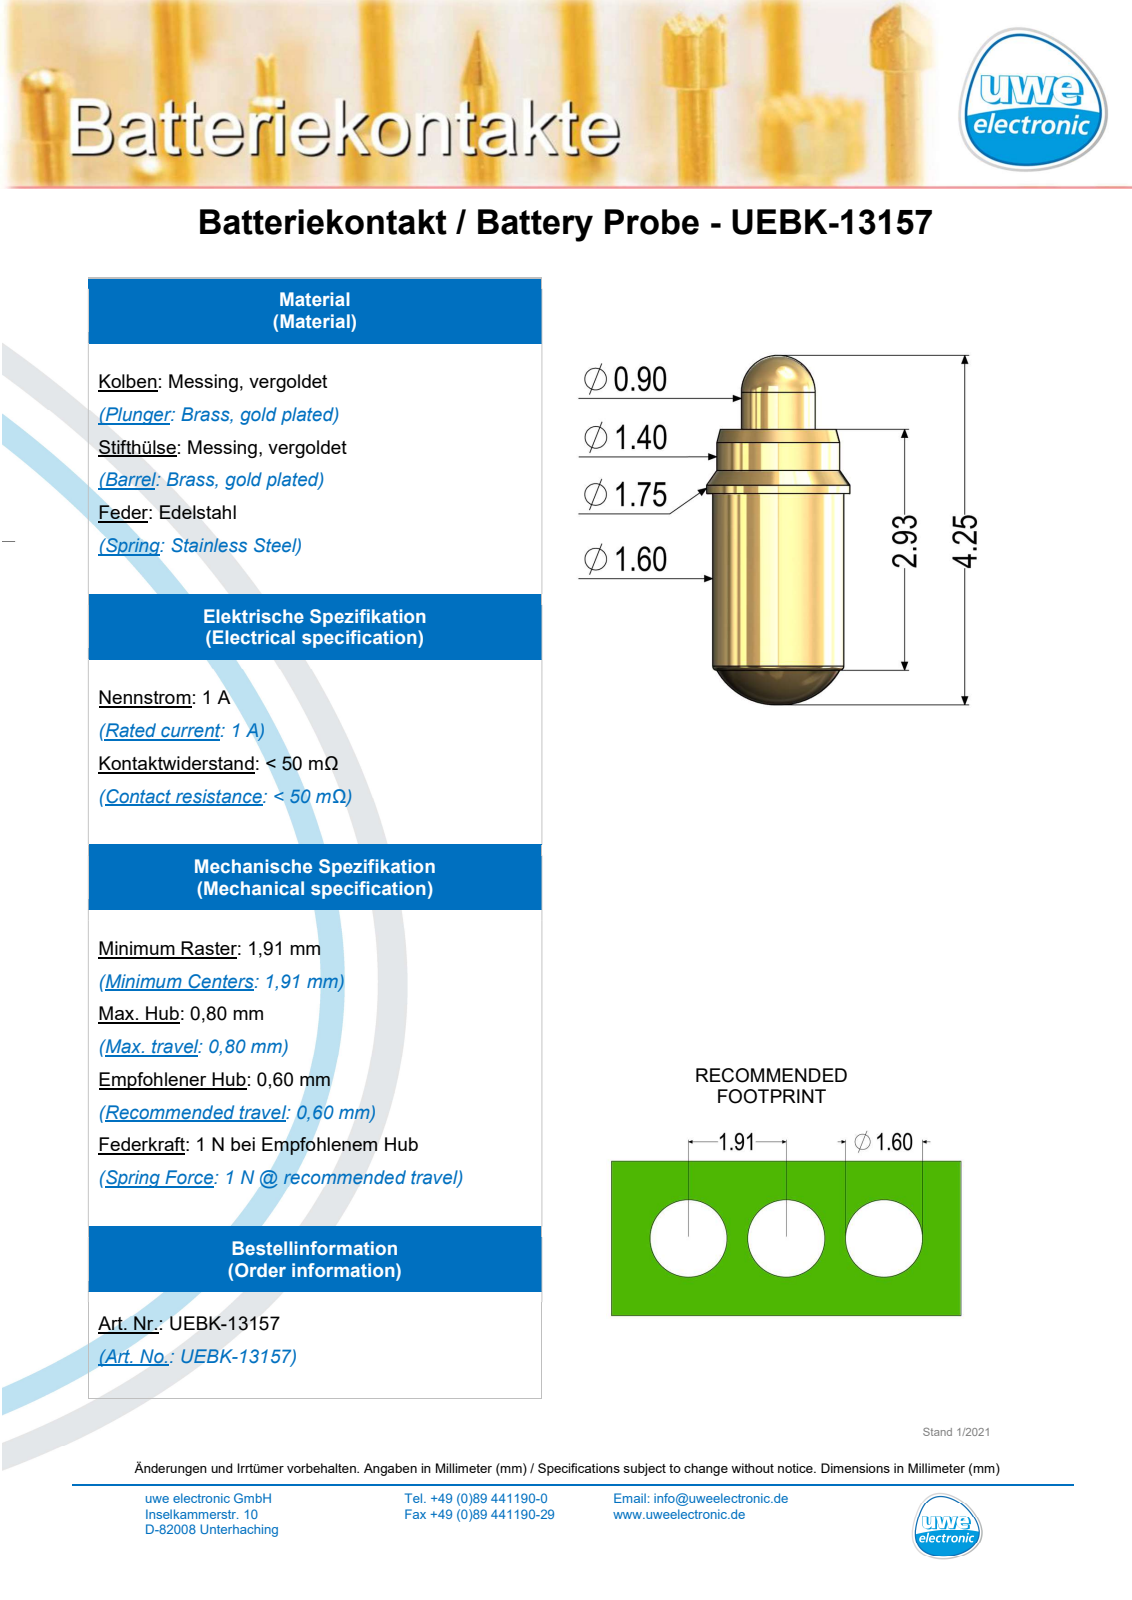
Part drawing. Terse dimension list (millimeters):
name: UEBK-13157_2017_09_06
written by: SolidWorks 2017 (AUTOMOTIVE_DESIGN)
unit: mm
bodies: 1 solid, 20 faces (2 planar, 8 cylindrical, 10 other)
size: 4.25 × 1.75 × 1.75
volume: 7 mm³; area: 21 mm²
bosses: 1× ⌀1.75, 1× ⌀1.6, 1× ⌀1.5, 1× ⌀0.9
face distances: 0.78
